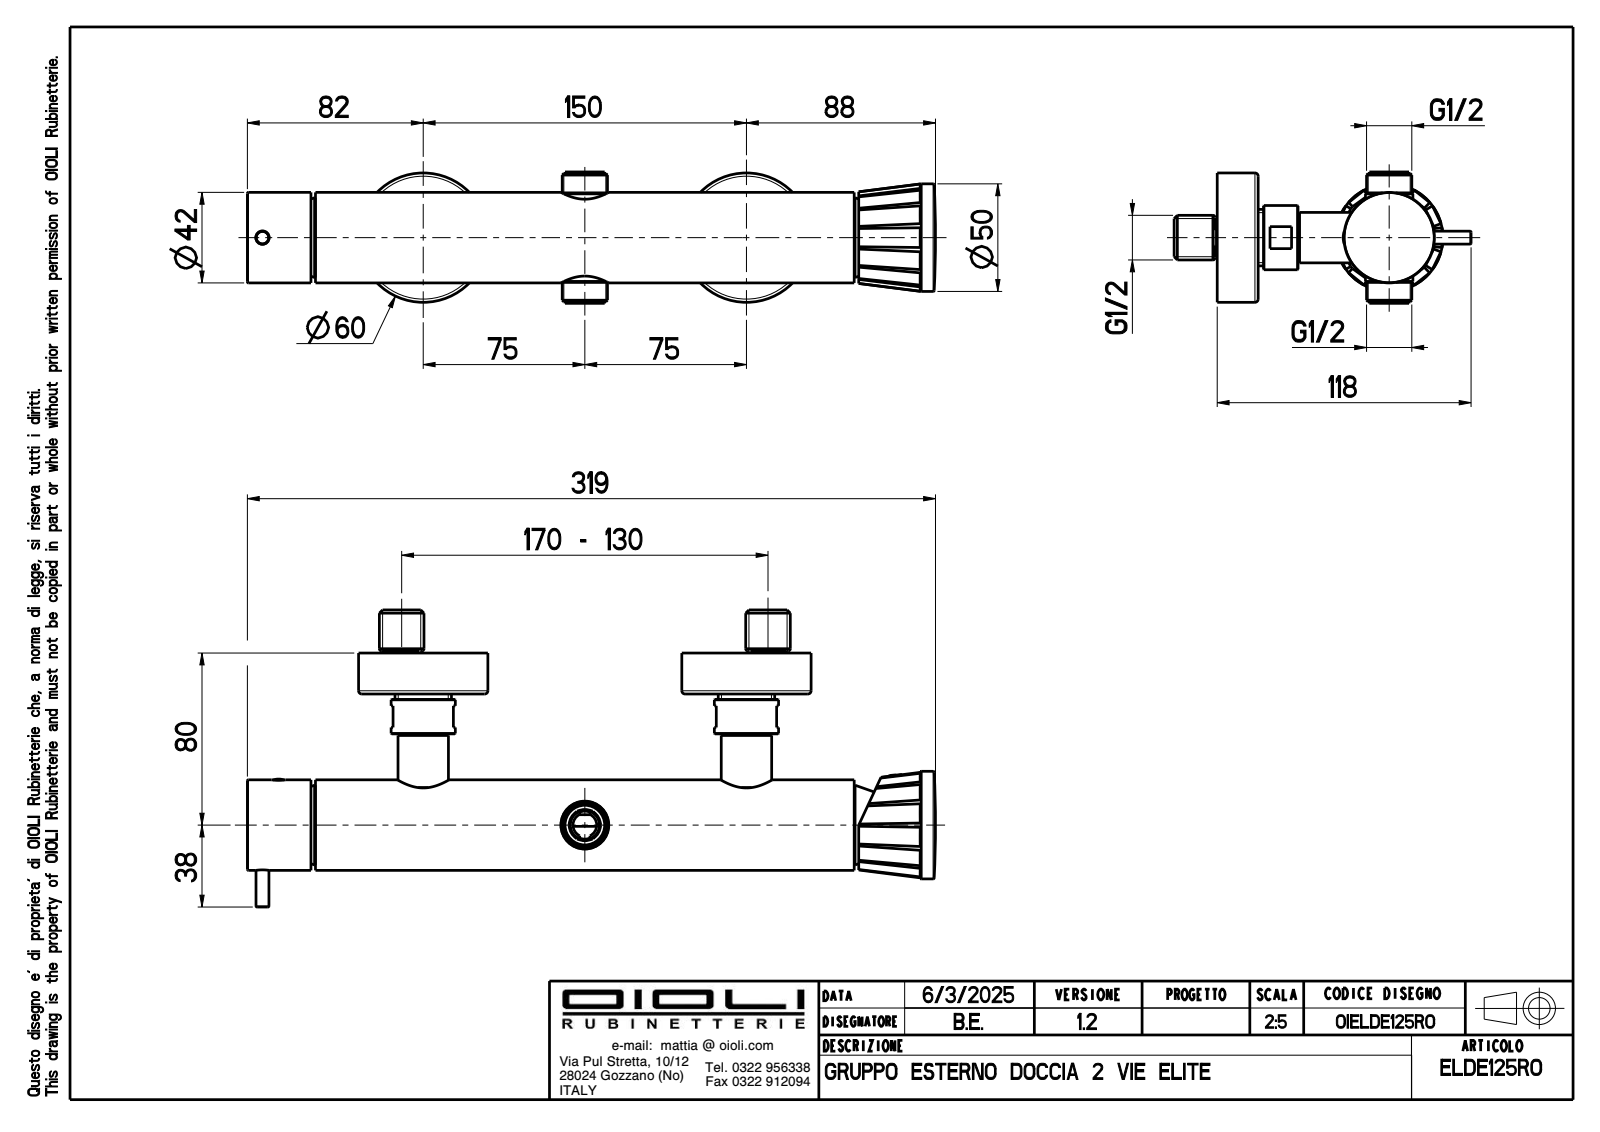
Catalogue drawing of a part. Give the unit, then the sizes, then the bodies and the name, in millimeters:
Units: millimetres
Overall size (bounding box): 319.32 × 137.8 × 60.94
Round holes (diameter × count): ⌀4 ×6, ⌀6 ×6, ⌀5 ×5, ⌀10 ×3, ⌀10.5 ×3, ⌀4.2 ×2, ⌀5.3 ×2, ⌀6.5 ×2, ⌀8 ×2, ⌀15.5 ×2, ⌀16.7 ×2, ⌀19 ×2
Round bosses / shafts (diameter × count): ⌀60 ×2, ⌀29.8 ×2, ⌀27.2 ×2, ⌀26.4 ×2, ⌀26.2 ×2, ⌀23.4 ×2, ⌀23.2 ×2, ⌀23 ×2
Partial cylindrical surfaces — rounded edges, fillets, slot ends (radius × count): R0.1 ×20, R0.5 ×15, R1 ×8, R7.5 ×4, R5.5 ×1
Main face-to-face distances: 0.7, 2.5, 13, 15.5, 316.2, 65.1, 11, 43.6, 248.1, 183
Hole centre spacings: 10.55, 4.24, 4.5, 6.28, 8.2, 8.97, 9.43, 10
Volume: 352 537 mm³ · Surface area: 166 136 mm²
Bodies: 20 solids, 1061 faces (297 planar, 361 cylindrical, 403 other)
Part name (STEP PRODUCT): OIBR00276; OIAQ00285; OIBR00998; OIAQ00028 (+8 more)
STEP written by: CREO PARAMETRIC BY PTC INC, 2024493 (CONFIG_CONTROL_DESIGN)
